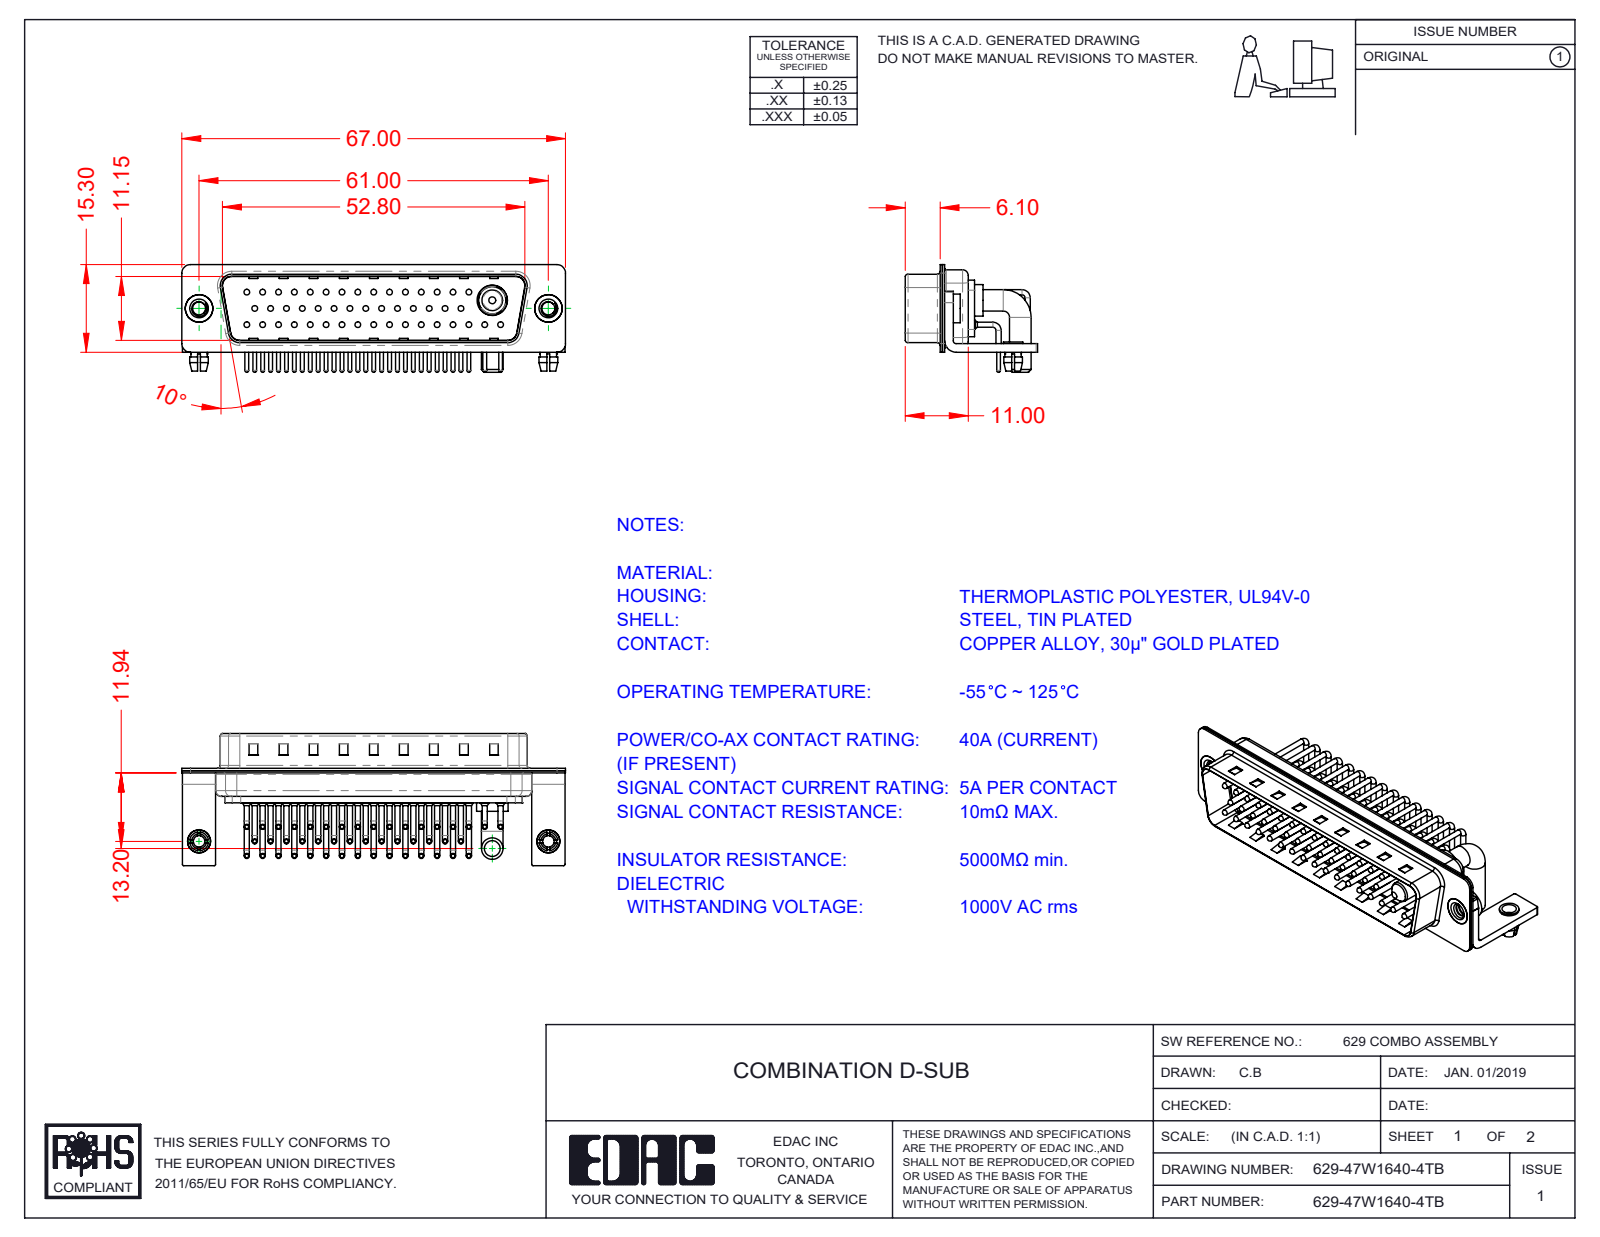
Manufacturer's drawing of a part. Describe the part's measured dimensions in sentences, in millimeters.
The part is named "629Combo Contact Row 1_50 Contacts; 629Combo Shell Rear_50 Contacts; Power Pin_40A RA 50; 629Combo Housing_47W1 (+7 more)". Its 3-D file was written by "SolidWorks 2020 (CONFIG_CONTROL_DESIGN)". It is 57 solids with 5655 faces: 3225 planar, 1874 cylindrical and 556 other. Overall it measures 67 by 23.1 by 18.8 millimeters. Its volume is 5 620 cubic millimeters and its surface area 13 778 square millimeters. Round holes: 48 of diameter 2, 46 of diameter 0.75, 46 of diameter 1.6, 2 of diameter 2.26, 2 of diameter 2.5, 2 of diameter 3.2, 2 of diameter 4, 2 of diameter 4.8, 1 of diameter 4.85, 1 of diameter 5.3. Round bosses or shafts: 92 of diameter 0.9, 46 of diameter 1.5, 46 of diameter 1, 46 of diameter 0.65, 2 of diameter 5, 2 of diameter 4.9, 2 of diameter 4, 2 of diameter 3.75. Partial cylindrical surfaces (rounded edges, fillets, slot ends): 46 of radius 1.01, 16 of radius 0.25, 16 of radius 1.5, 13 of radius 2, 9 of radius 0.5, 8 of radius 1.6, 4 of radius 0.6, 4 of radius 0.65. The main face-to-face distances are 0.4, 1.5, 11.55, 5.6, 5.2, 4.1, 0.8, 6, 1.9, 0.78. The hole center spacings are 2.77, 3.16, 5.54, 8.31, 11.08, 13.85, 16.62, 19.39.
